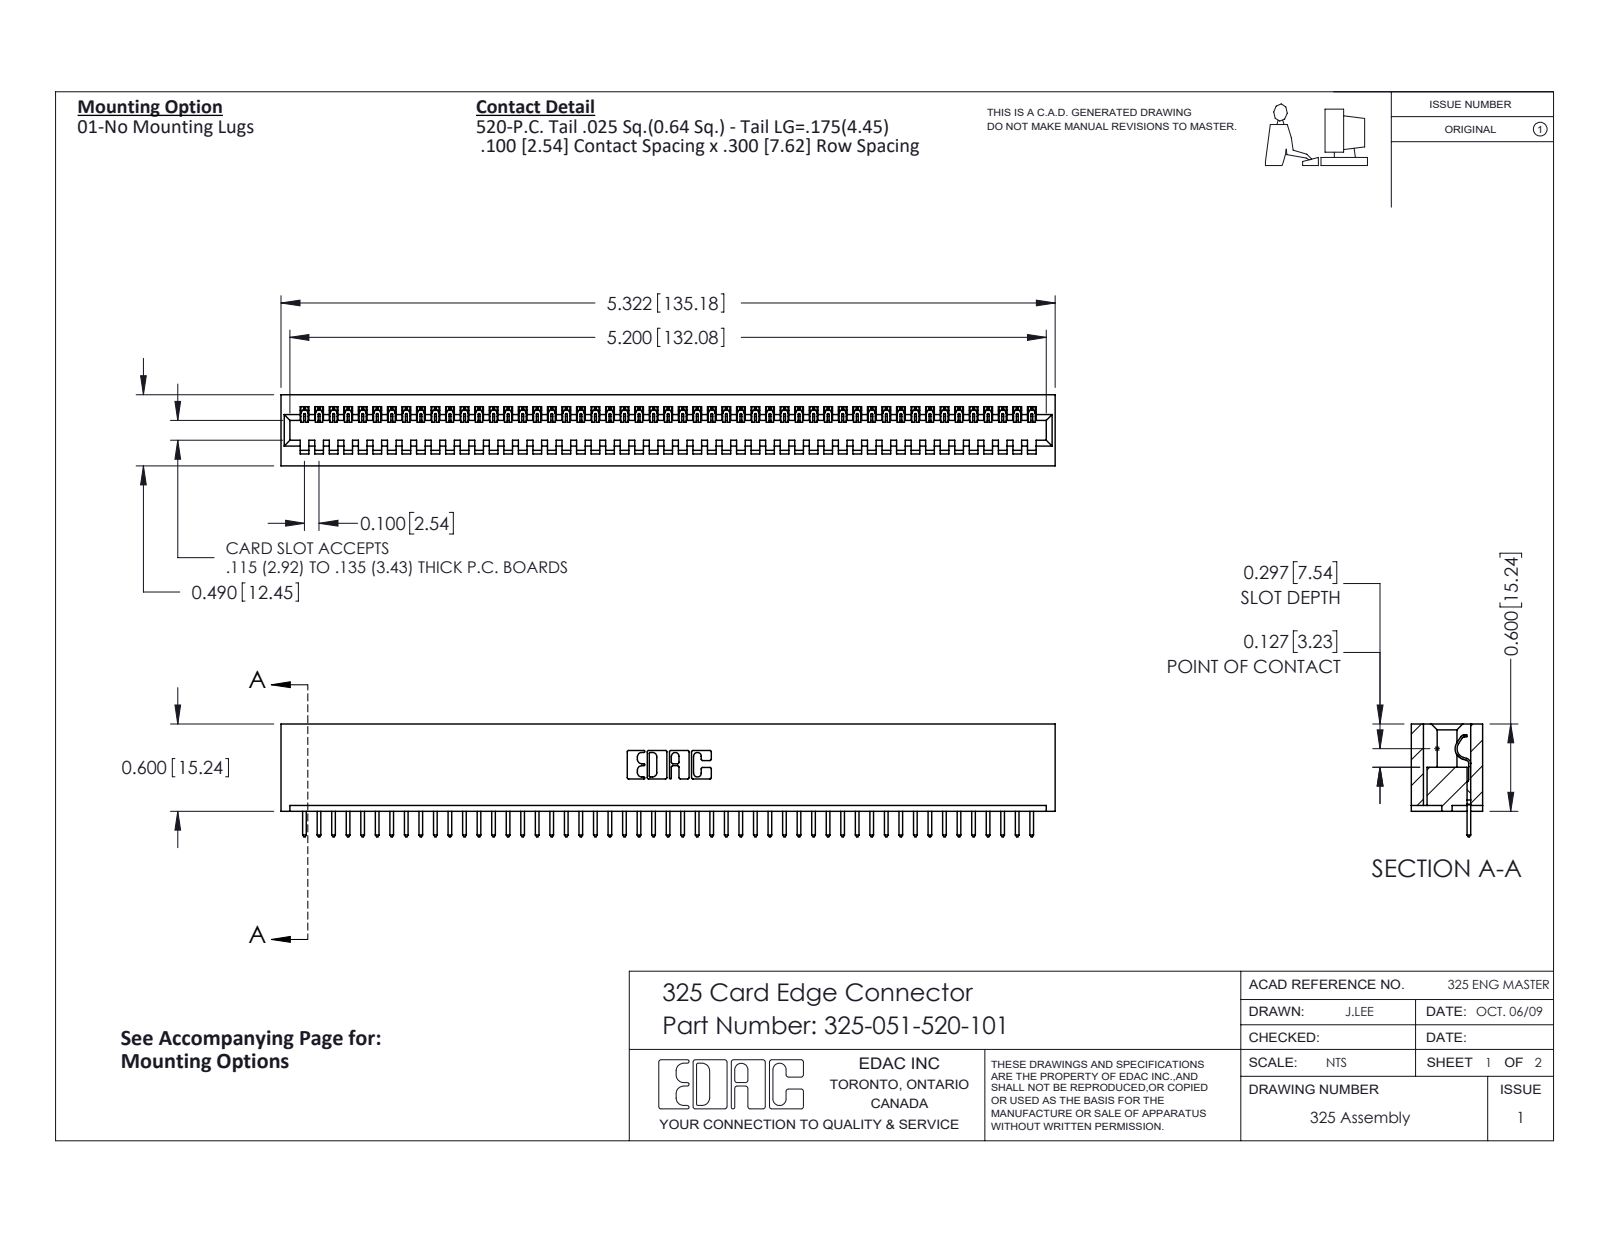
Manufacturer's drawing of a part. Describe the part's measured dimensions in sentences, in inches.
The part is named "325-051-520-101; 325 Part_Lugless; 325-292-001_325-293-120". Its 3-D file was written by "SolidWorks 2016 (CONFIG_CONTROL_DESIGN)". It is 52 solids with 3064 faces: 2208 planar, 856 cylindrical and 0 other. Overall it measures 5.322 by 0.775 by 0.49 inches. Its volume is 1.078 cubic inches and its surface area 30.09 square inches. Partial cylindrical surfaces (rounded edges, fillets, slot ends): 102 of radius 0.006, 102 of radius 0.01, 22 of radius 0.01, 6 of radius 0.007, 6 of radius 0.031, 3 of radius 0.026, 1 of radius 0.014, 1 of radius 0.022. The main face-to-face distances are 0.083, 0.407, 0.49, 0.3, 0.107, 0.383, 0.025, 0.325, 0.56, 0.263.
